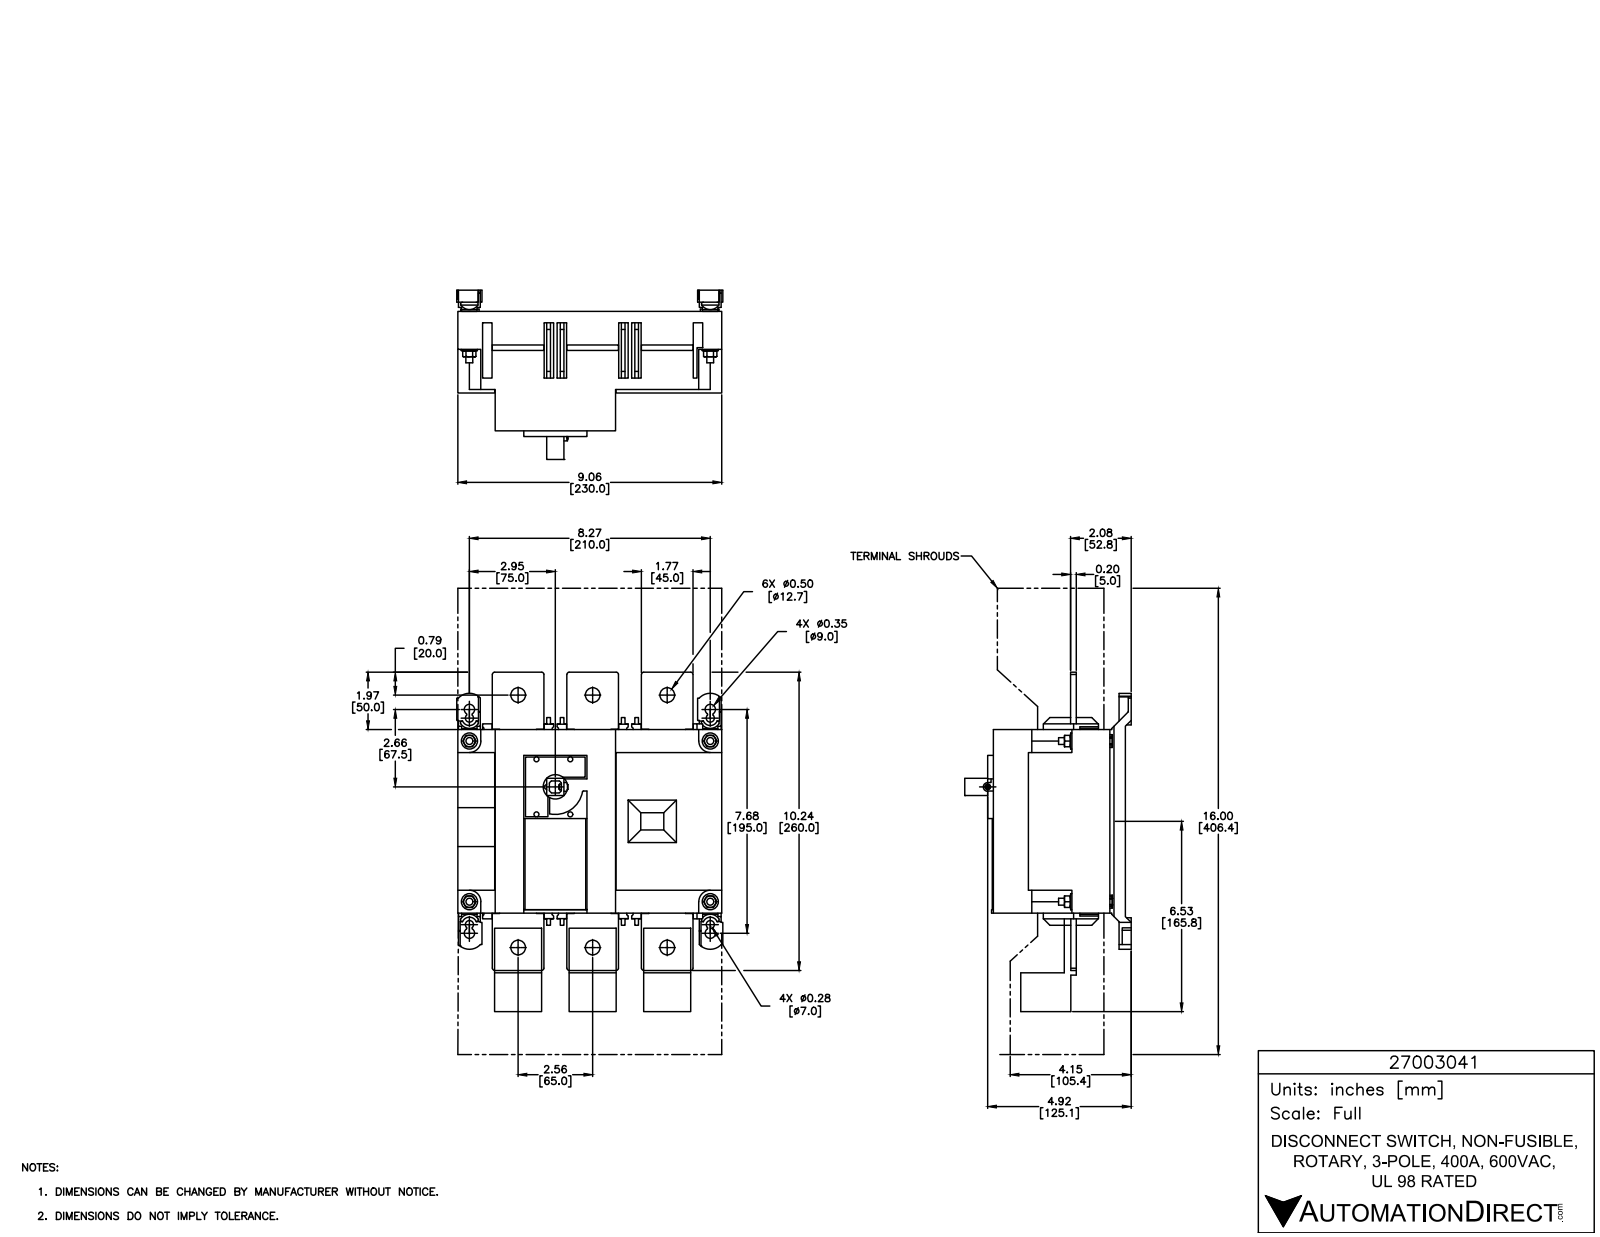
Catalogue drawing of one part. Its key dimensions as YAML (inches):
part_name: "27003041"
step_written_by: "SolidWorks 2018 (AUTOMOTIVE_DESIGN)"
units: inches
bodies: {solids: 16, faces: 993, planar: 544, cylindrical: 332, other: 117}
overall_size: [10.236, 9.134, 5.811]
volume: 199.2
surface_area: 381.7
round_holes:
  - {diameter: 0.248, count: 12}
  - {diameter: 0.5, count: 6}
  - {diameter: 0.167, count: 4}
  - {diameter: 0.169, count: 4}
  - {diameter: 0.197, count: 4}
  - {diameter: 0.26, count: 4}
  - {diameter: 0.276, count: 4}
  - {diameter: 0.313, count: 4}
  - {diameter: 0.331, count: 4}
  - {diameter: 0.354, count: 4}
  - {diameter: 0.472, count: 4}
  - {diameter: 0.098, count: 3}
round_bosses_or_shafts:
  - {diameter: 0.551, count: 4}
  - {diameter: 0.315, count: 4}
  - {diameter: 0.244, count: 4}
  - {diameter: 0.236, count: 4}
  - {diameter: 0.833, count: 1}
  - {diameter: 0.197, count: 1}
partial_cylinders:
  - {radius: 0.039, count: 29}
  - {radius: 0.02, count: 19}
  - {radius: 0.079, count: 12}
  - {radius: 0.344, count: 12}
  - {radius: 0.217, count: 8}
  - {radius: 0.049, count: 4}
  - {radius: 0.138, count: 4}
  - {radius: 0.236, count: 4}
face_to_face_distances: [1.457, 6.299, 1.343, 1.154, 0.189, 2.799, 1.646, 2.756, 1.299, 9.055]
hole_center_spacings: [2.559, 5.512, 0.116, 0.632, 0.748, 5.118, 5.513, 5.548]
